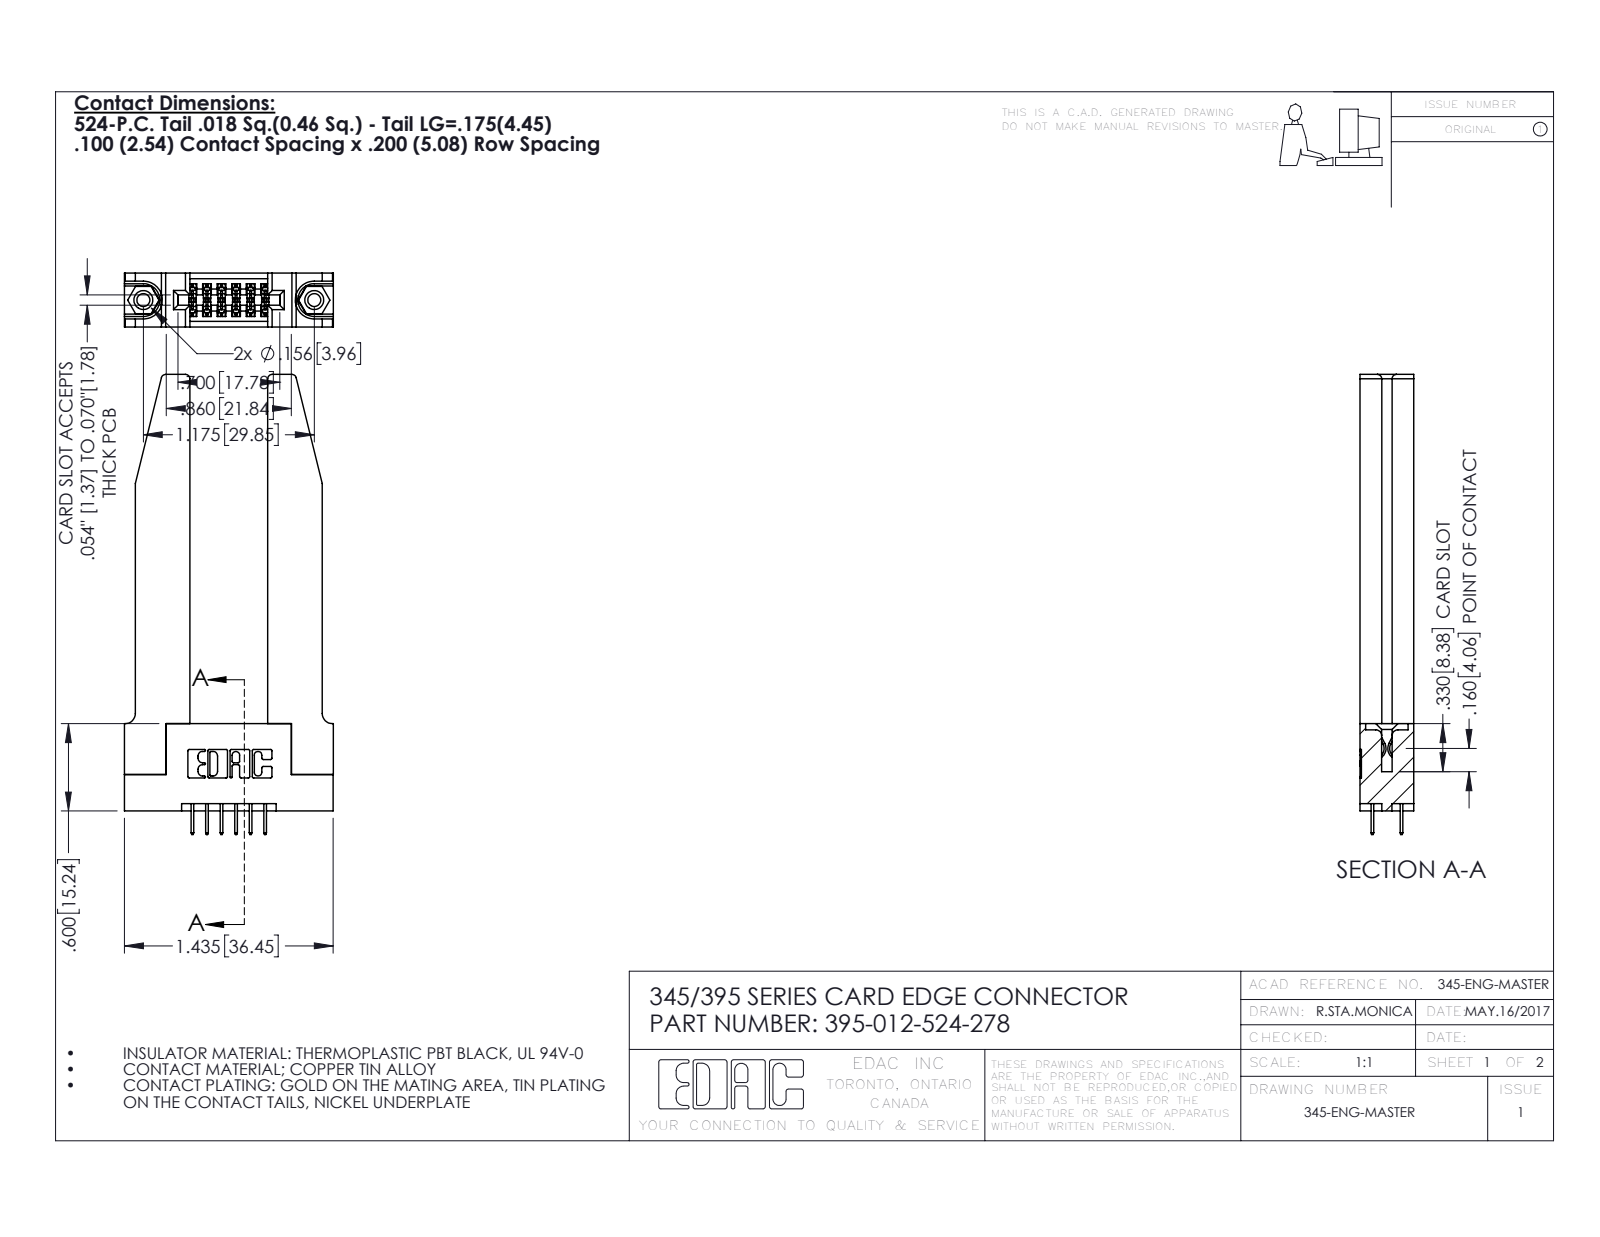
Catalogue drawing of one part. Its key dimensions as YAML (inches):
part_name: "345-220-078_345-220-078; 395-012-524-278; 345-250-001_345-250-001-102; 345 Part_Flush Mounting Lugs - 0.156 Dia-TH (+1 more)"
step_written_by: "SolidWorks 2016 (CONFIG_CONTROL_DESIGN)"
units: inches
bodies: {solids: 17, faces: 1008, planar: 690, cylindrical: 266, other: 52}
overall_size: [3.162, 1.436, 0.37]
volume: 0.669
surface_area: 16.76
round_holes:
  - {diameter: 0.089, count: 2}
  - {diameter: 0.125, count: 2}
  - {diameter: 0.156, count: 2}
  - {diameter: 0.064, count: 1}
round_bosses_or_shafts:
  - {diameter: 0.155, count: 2}
partial_cylinders:
  - {radius: 0.01, count: 22}
  - {radius: 0.006, count: 18}
  - {radius: 0.03, count: 8}
  - {radius: 0.007, count: 6}
  - {radius: 0.031, count: 6}
  - {radius: 0.026, count: 3}
  - {radius: 0.014, count: 2}
  - {radius: 0.019, count: 2}
face_to_face_distances: [0.37, 0.15, 0.22, 0.535, 0.072, 0.148, 0.077, 0.298, 0.2, 0.095]
hole_center_spacings: [0.27, 0.946, 1.175]
